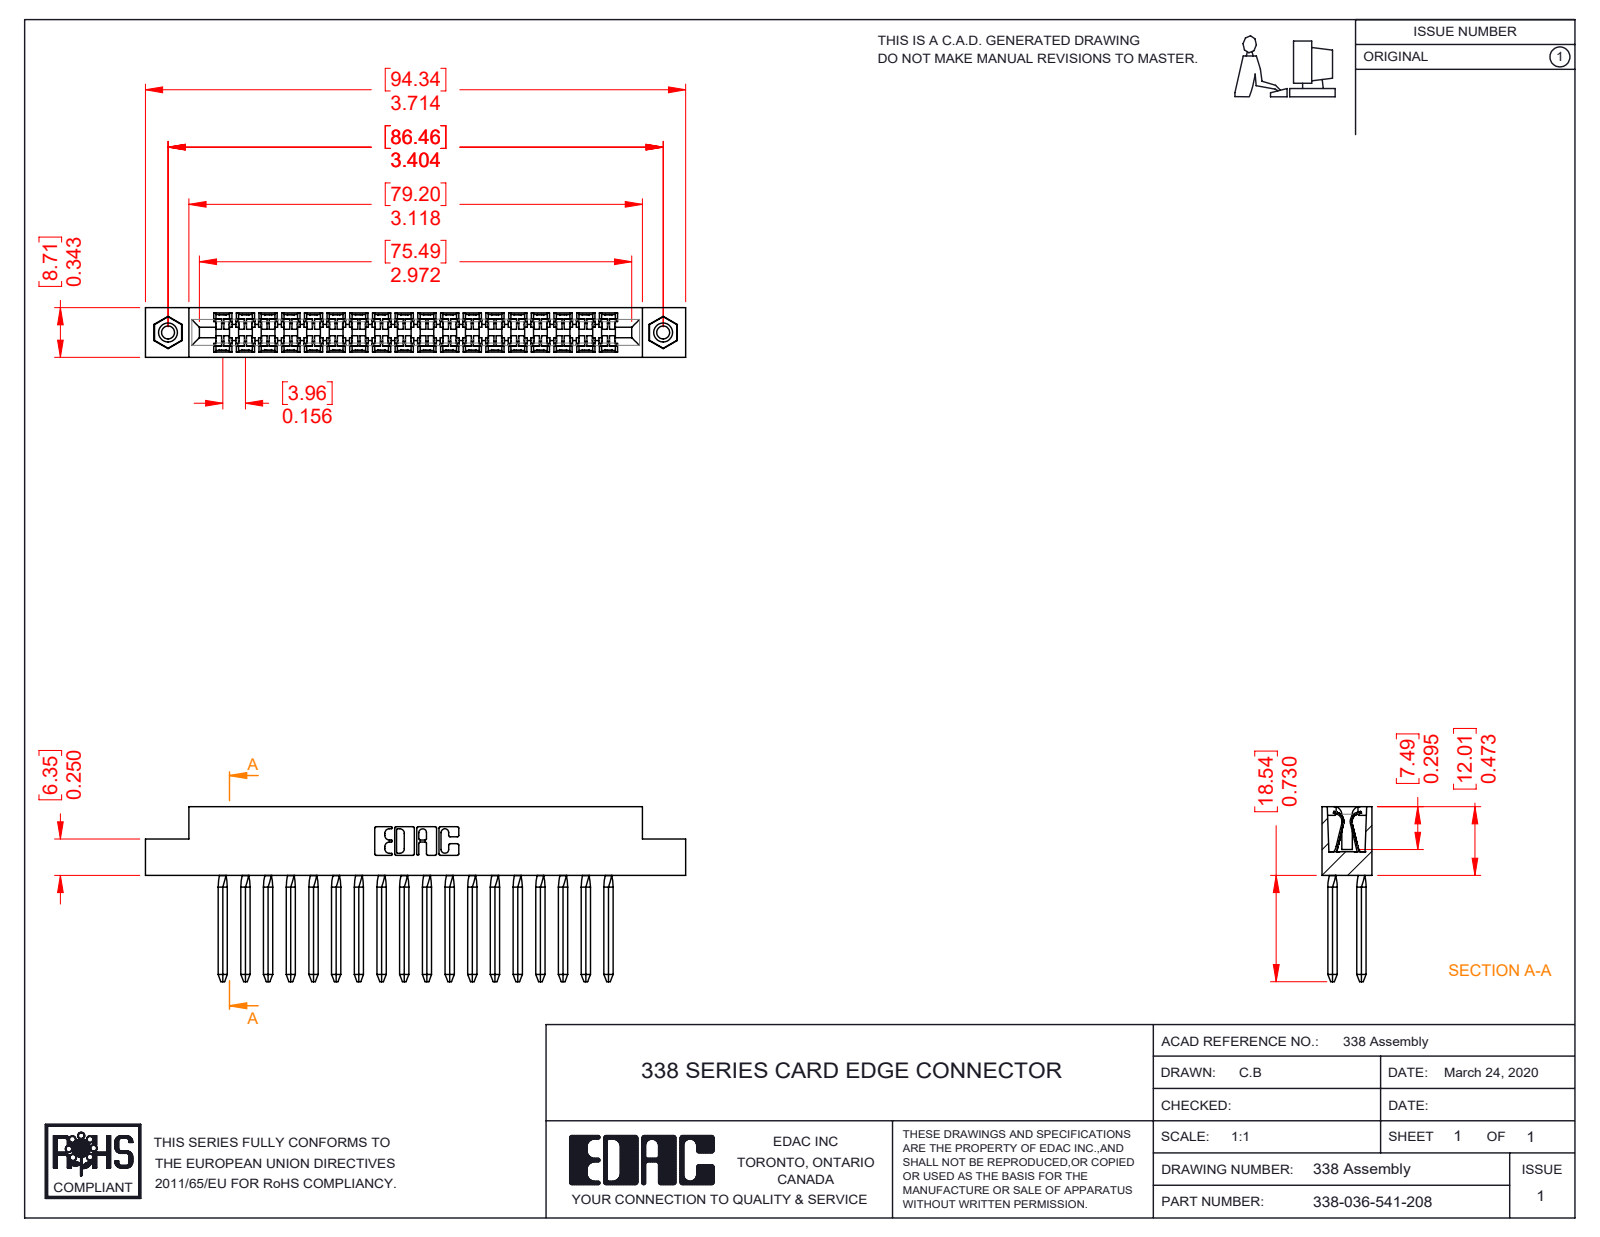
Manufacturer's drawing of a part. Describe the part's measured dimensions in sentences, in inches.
The part is named "338-290-001_541; 338-036-541-208; 345-250-001_345-250-003-102; 338-210-001_338-210-018-004". Its 3-D file was written by "SolidWorks 2016 (CONFIG_CONTROL_DESIGN)". It is 39 solids with 2566 faces: 1774 planar, 632 cylindrical and 160 other. Overall it measures 3.714 by 1.203 by 0.343 inches. Its volume is 0.439 cubic inches and its surface area 20.29 square inches. Round holes: 2 of diameter 0.089, 2 of diameter 0.125, 2 of diameter 0.156. Round bosses or shafts: 2 of diameter 0.155. Partial cylindrical surfaces (rounded edges, fillets, slot ends): 110 of radius 0.025, 36 of radius 0.008, 30 of radius 0.055, 30 of radius 0.067, 28 of radius 0.1, 22 of radius 0.01, 6 of radius 0.007, 6 of radius 0.031. The main face-to-face distances are 0.343, 0.156, 0.624, 0.11, 0.78, 0.468, 0.135, 0.207, 0.221, 0.312. The hole center spacings are 3.404.
